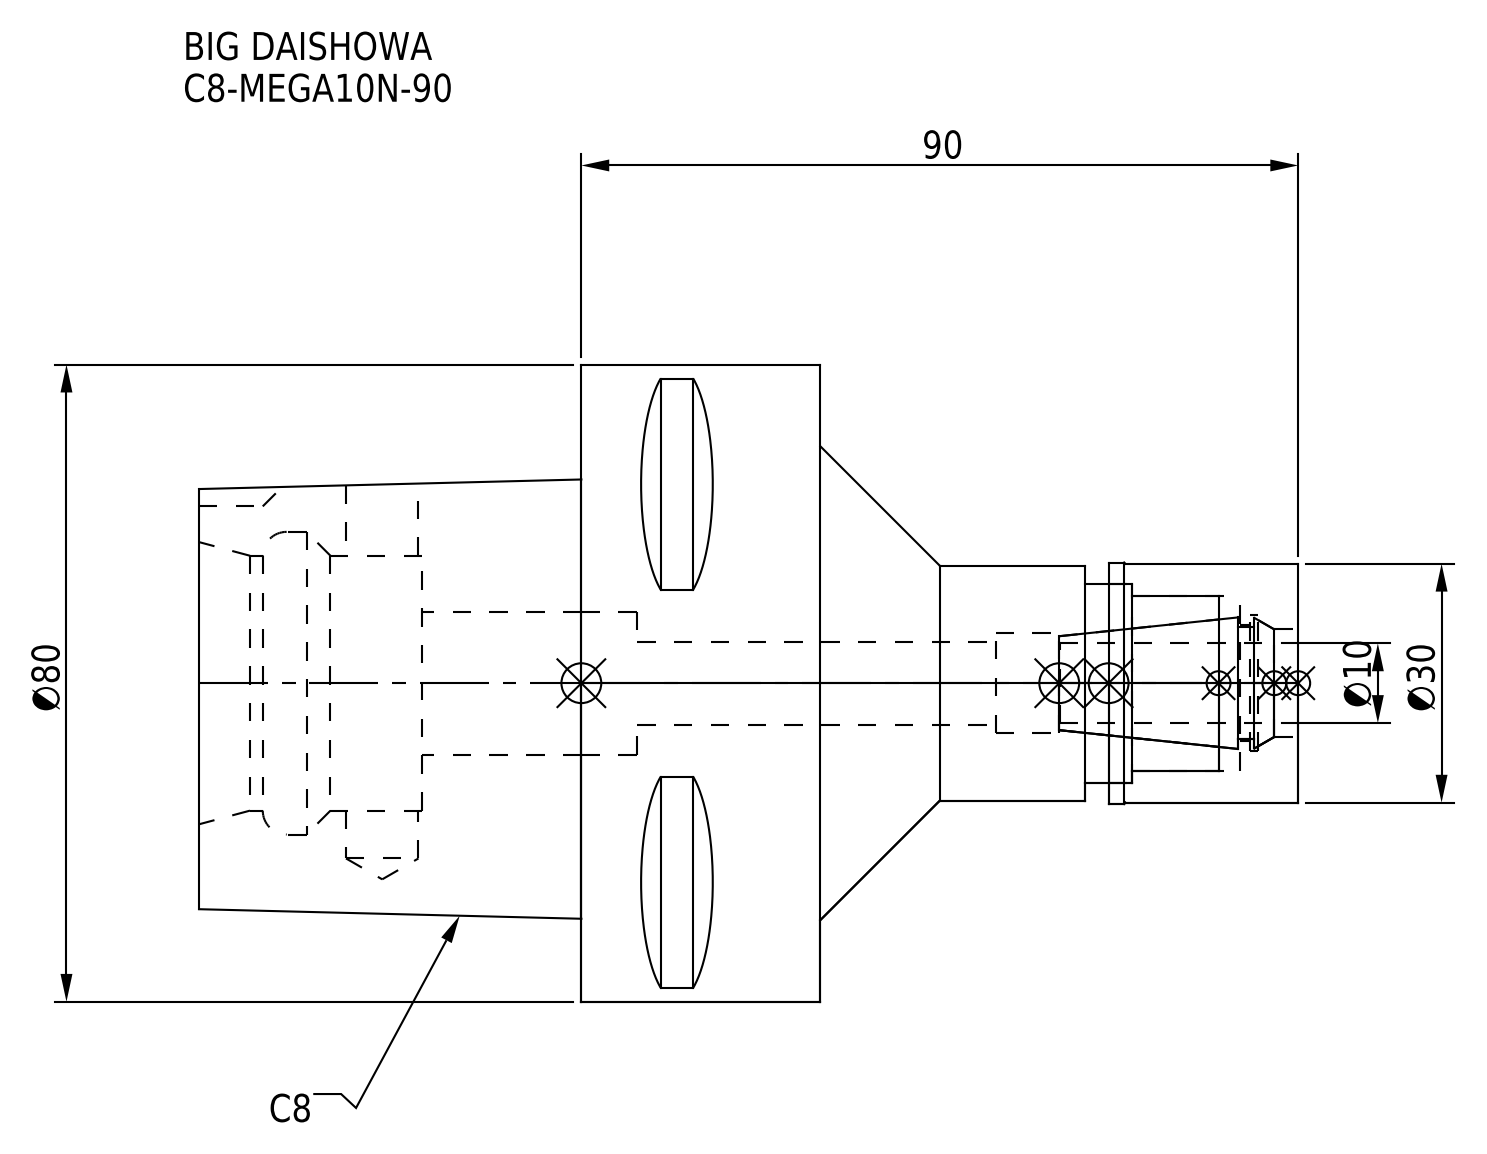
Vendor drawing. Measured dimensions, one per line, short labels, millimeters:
name: C8-MEGA10N-90-100-FreeParts; C8-MEGA10N-90_1.stp; C8-MEGA10N-90; C8-MEGA10N-90-100_ASM.stp (+3 more)
written by: SolidWorks 2019 (CONFIG_CONTROL_DESIGN)
unit: mm
bodies: 2 solids, 95 faces (38 planar, 39 cylindrical, 18 other)
size: 138 × 80 × 80
volume: 268 046 mm³; area: 42 209 mm²
holes: 1× ⌀9.1, 1× ⌀10.4, 1× ⌀12.5, 1× ⌀13.5, 1× ⌀14.5, 1× ⌀17, 1× ⌀18, 1× ⌀22, 1× ⌀25, 1× ⌀32, 1× ⌀38
bosses: 1× ⌀80, 1× ⌀30.3, 1× ⌀30, 1× ⌀29.5
rounds: 1× R6
face distances: 30, 78, 48, 50, 28, 20, 60, 90, 138, 110
